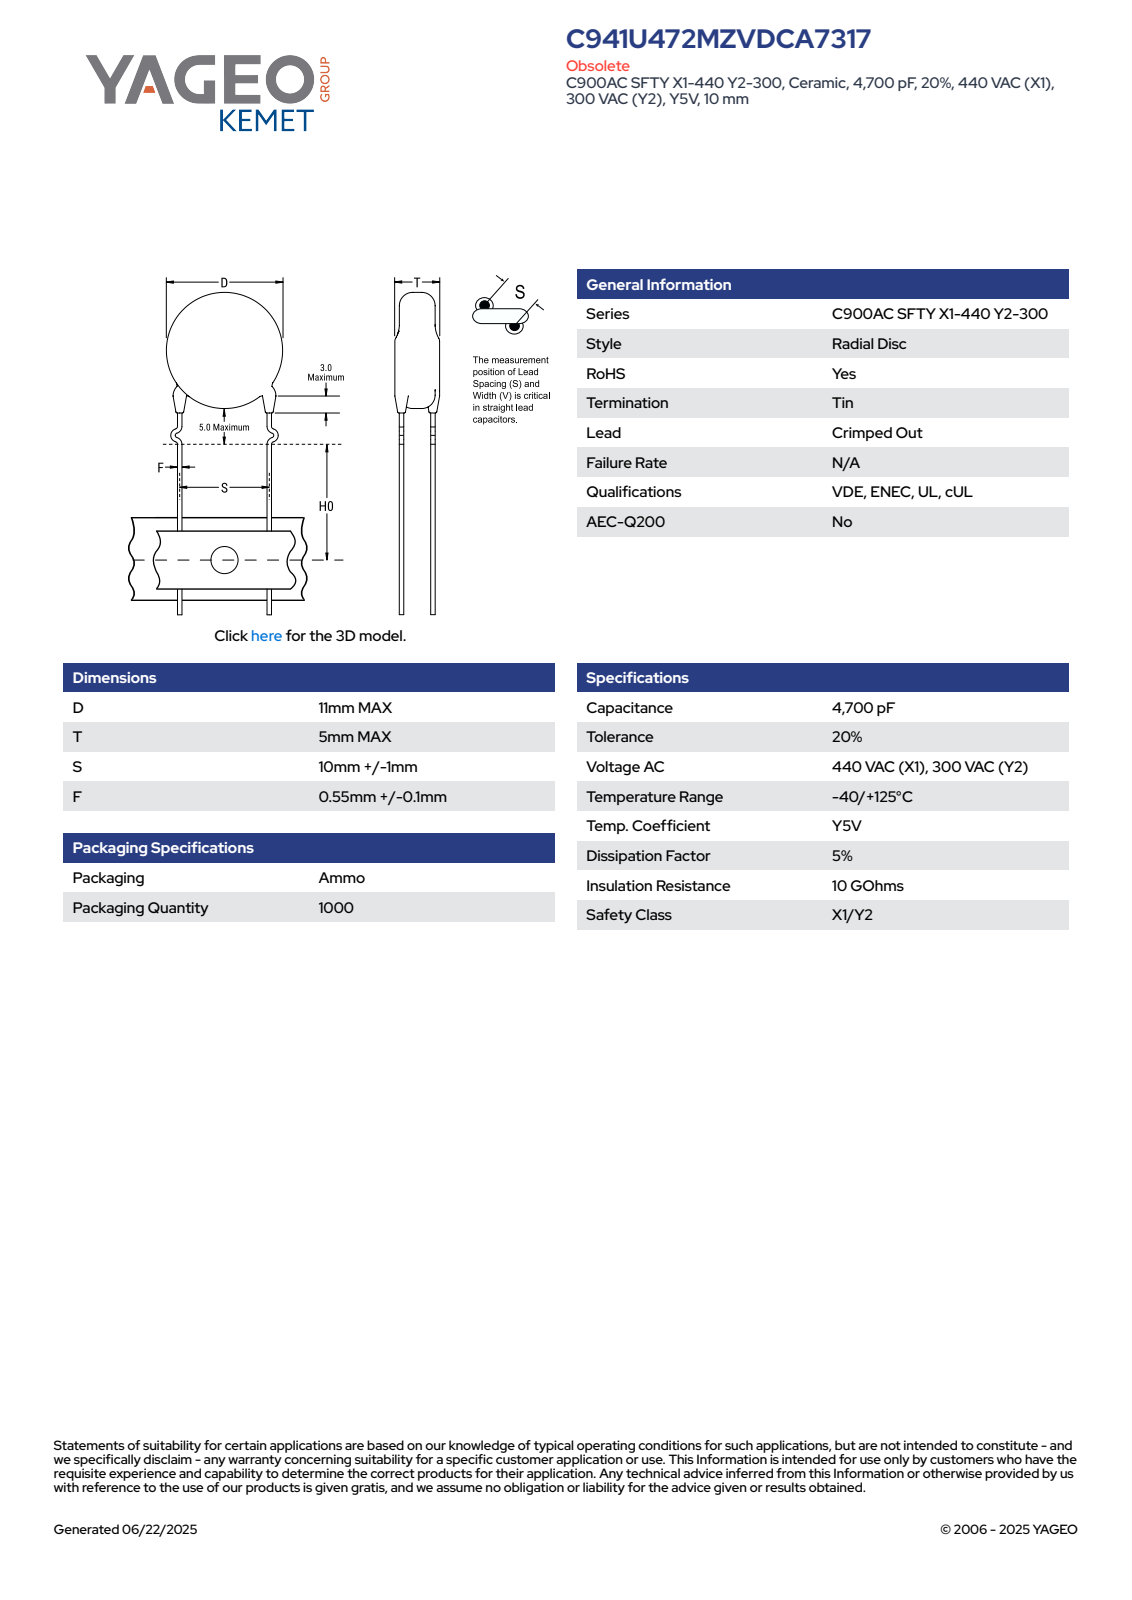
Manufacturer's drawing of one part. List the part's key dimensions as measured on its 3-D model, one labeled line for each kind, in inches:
Part name (STEP PRODUCT): CCD_KCOC900_D11T5S10LL20F0.55
STEP written by: SolidWorks 2014 (AUTOMOTIVE_DESIGN)
Units: inches
Bodies: 4 solids, 87 faces (63 planar, 6 cylindrical, 18 other)
Overall size (bounding box): 1.417 × 0.585 × 0.201
Volume: 0.03 in³ · Surface area: 0.733 in²
Round bosses / shafts (diameter × count): ⌀0.047 ×2, ⌀0.433 ×1
Main face-to-face distances: 0.197, 0.045, 0.239, 0.194, 0.013, 0.036, 0.184, 0.093, 0.133, 0.139
